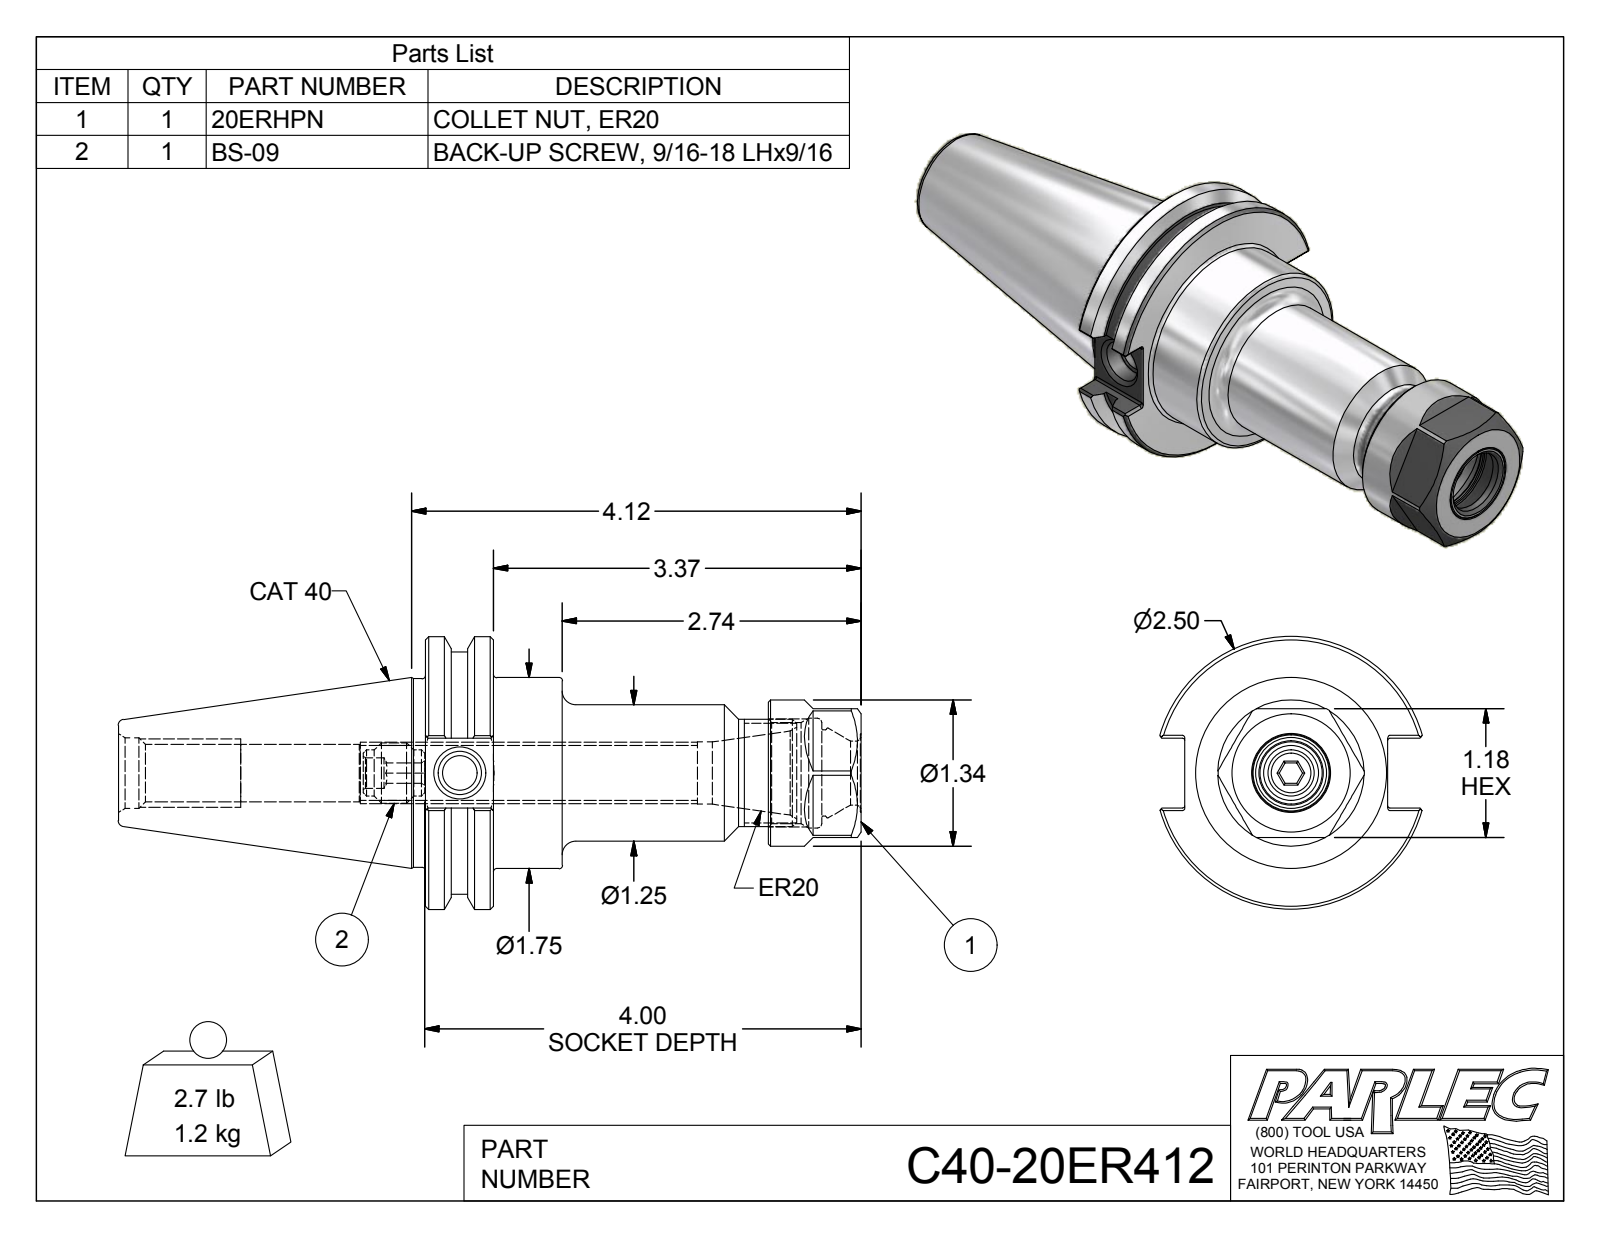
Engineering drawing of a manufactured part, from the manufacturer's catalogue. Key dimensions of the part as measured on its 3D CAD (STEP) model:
Part name (STEP PRODUCT): C40-20ER412; C40-20ER4-1; 20ERHPN; BS-09
STEP written by: Autodesk Inventor 2012 (AUTOMOTIVE_DESIGN)
Units: inches
Bodies: 3 solids, 144 faces (63 planar, 38 cylindrical, 43 other)
Overall size (bounding box): 6.808 × 2.5 × 2.403
Volume: 10.04 in³ · Surface area: 55.62 in²
Round holes (diameter × count): ⌀0.281 ×1, ⌀0.315 ×1, ⌀0.399 ×1, ⌀0.502 ×1, ⌀0.525 ×1, ⌀0.527 ×1, ⌀0.57 ×1, ⌀0.587 ×1, ⌀0.648 ×1, ⌀0.79 ×1, ⌀0.926 ×1, ⌀1.005 ×1
Round bosses / shafts (diameter × count): ⌀2.5 ×1, ⌀2.219 ×1, ⌀1.75 ×1, ⌀1.73 ×1, ⌀1.34 ×1, ⌀1.25 ×1, ⌀0.984 ×1, ⌀0.555 ×1
Partial cylindrical surfaces — rounded edges, fillets, slot ends (radius × count): R0.02 ×12
Main face-to-face distances: 0.625, 1.18, 3.145, 2.52, 3.995, 3.37, 0.85, 0.63, 1.255, 1.89
